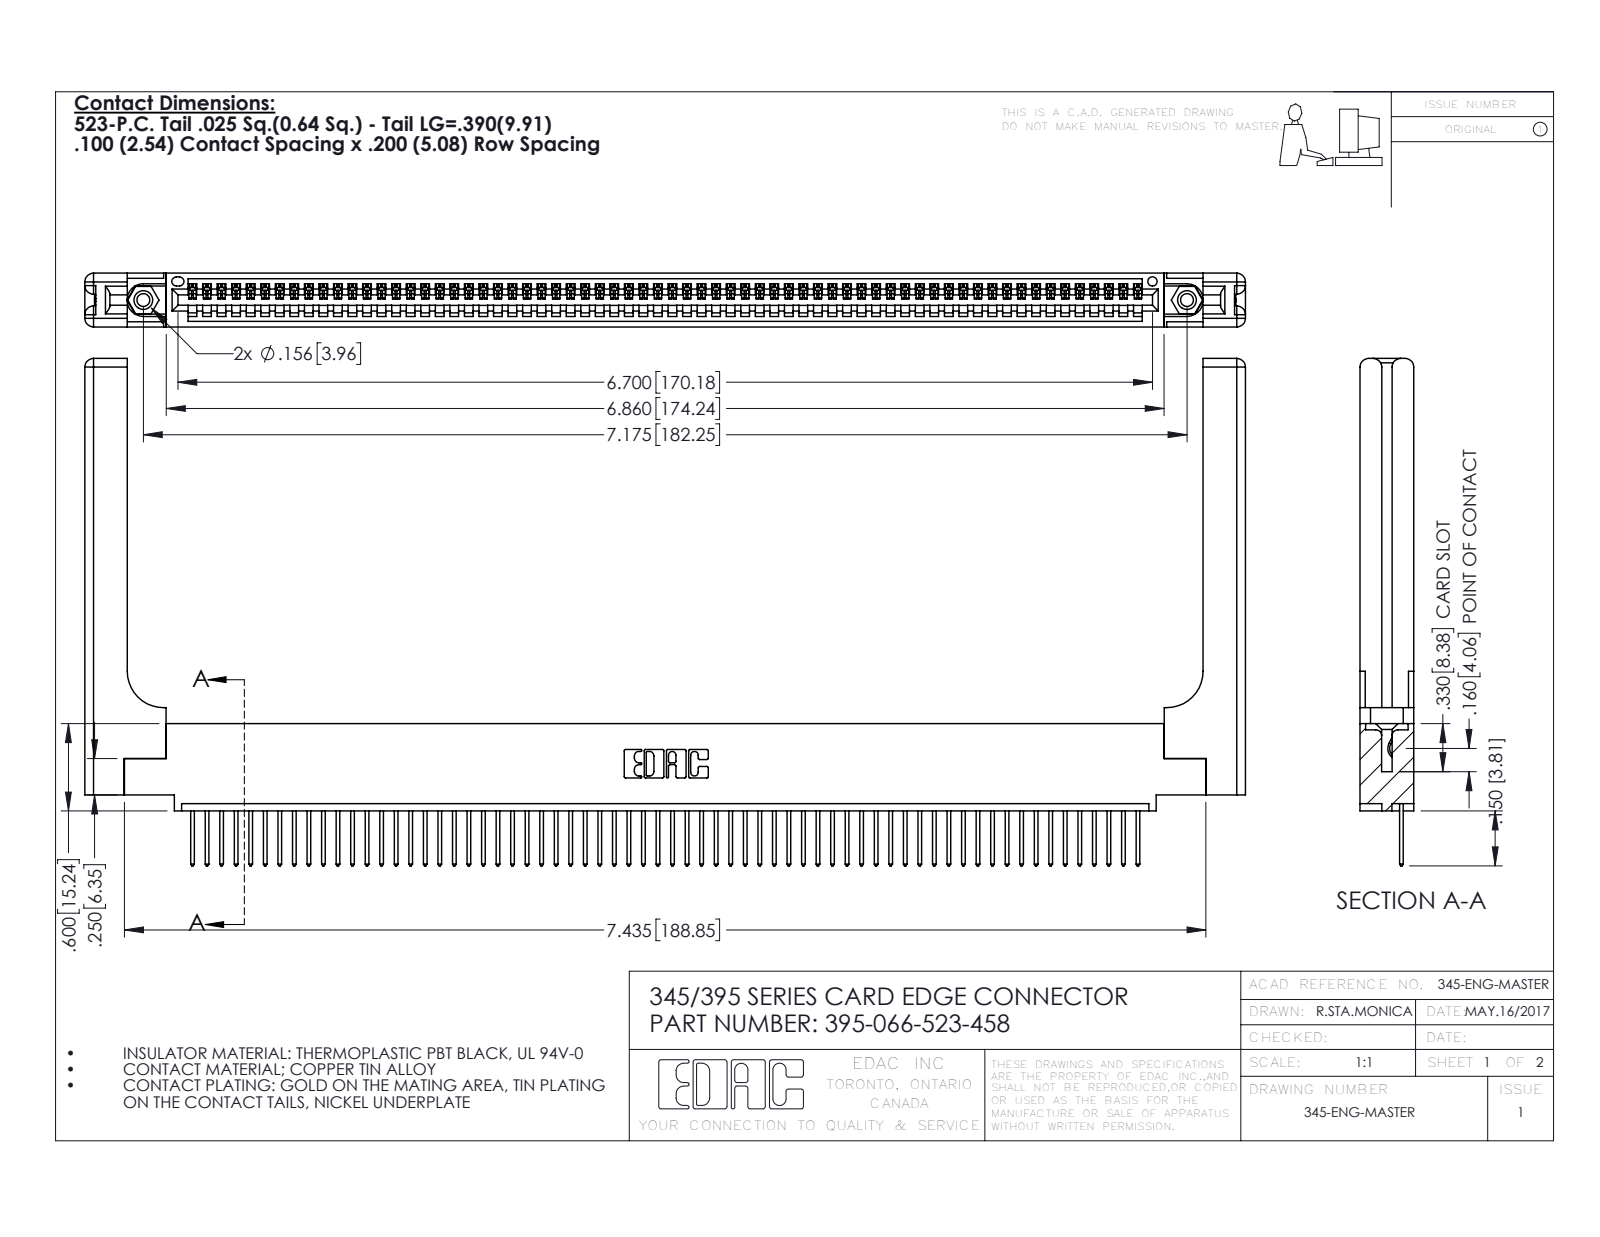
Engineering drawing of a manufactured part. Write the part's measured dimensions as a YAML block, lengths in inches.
part_name: "395-066-523-458; 345-250-001_345-250-001-102; 345-292-001_345-293-123; 345 Part_0.110 Offset - 0.156 Dia-TH (+1 more)"
step_written_by: "SolidWorks 2016 (CONFIG_CONTROL_DESIGN)"
units: inches
bodies: {solids: 71, faces: 4214, planar: 2872, cylindrical: 1282, other: 60}
overall_size: [7.979, 3.487, 0.37]
volume: 1.7
surface_area: 48.82
round_holes:
  - {diameter: 0.089, count: 2}
  - {diameter: 0.125, count: 2}
  - {diameter: 0.156, count: 2}
  - {diameter: 0.064, count: 1}
round_bosses_or_shafts:
  - {diameter: 0.155, count: 2}
partial_cylinders:
  - {radius: 0.006, count: 132}
  - {radius: 0.01, count: 132}
  - {radius: 0.01, count: 22}
  - {radius: 0.06, count: 16}
  - {radius: 0.007, count: 6}
  - {radius: 0.031, count: 6}
  - {radius: 0.026, count: 3}
  - {radius: 0.03, count: 2}
face_to_face_distances: [0.072, 0.298, 0.37, 0.098, 0.272, 0.025, 0.2, 0.225, 0.148, 0.15]
hole_center_spacings: [0.27, 6.939, 7.175]
